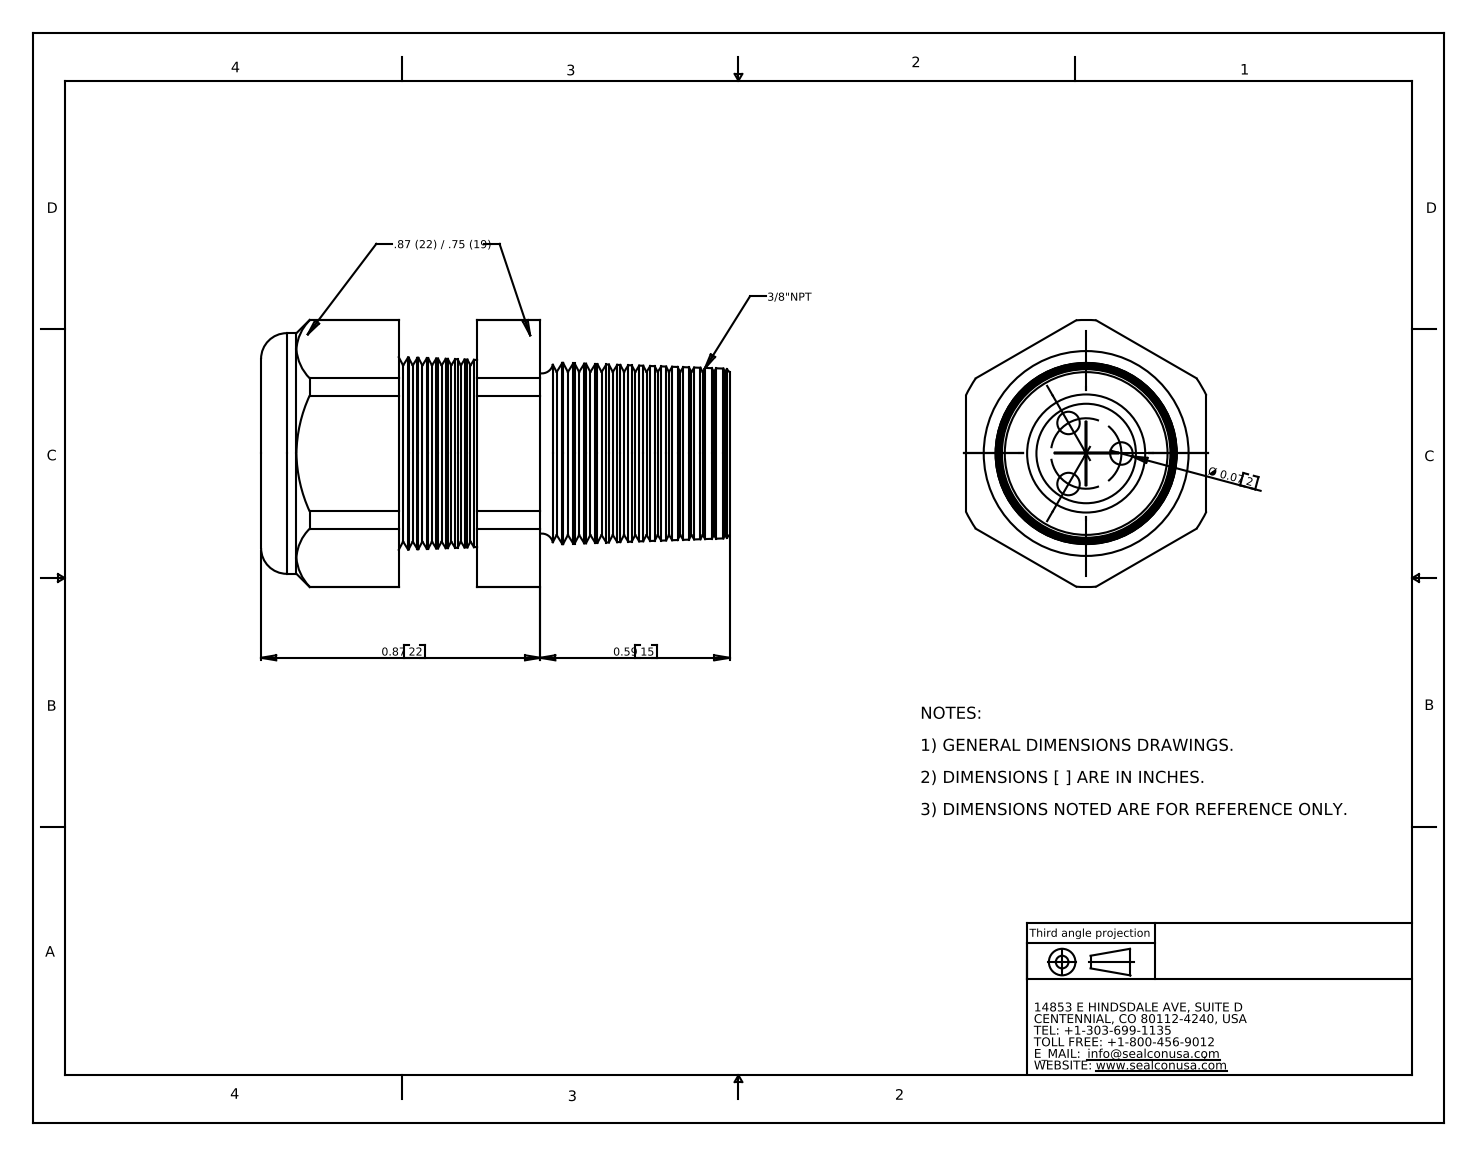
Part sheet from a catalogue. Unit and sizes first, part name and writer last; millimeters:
Units: millimetres
Overall size (bounding box): 37.1 × 21.2 × 19.1
Round holes (diameter × count): ⌀1.8 ×3, ⌀7.4 ×1, ⌀7.9 ×1
Round bosses / shafts (diameter × count): ⌀19.1 ×1
Partial cylindrical surfaces — rounded edges, fillets, slot ends (radius × count): R10.6 ×1
Main face-to-face distances: 19.1, 17.1, 10.9, 6.2, 19.1, 22.1, 11.2, 5, 37.1, 26.2
Hole centre spacings: 4.9, 2.8, 2.8
Volume: 6 050 mm³ · Surface area: 4 529 mm²
Bodies: 2 solids, 204 faces (20 planar, 26 cylindrical, 158 other)
Part name (STEP PRODUCT): CD09N7-BK
STEP written by: SolidWorks 2007 (CONFIG_CONTROL_DESIGN)
